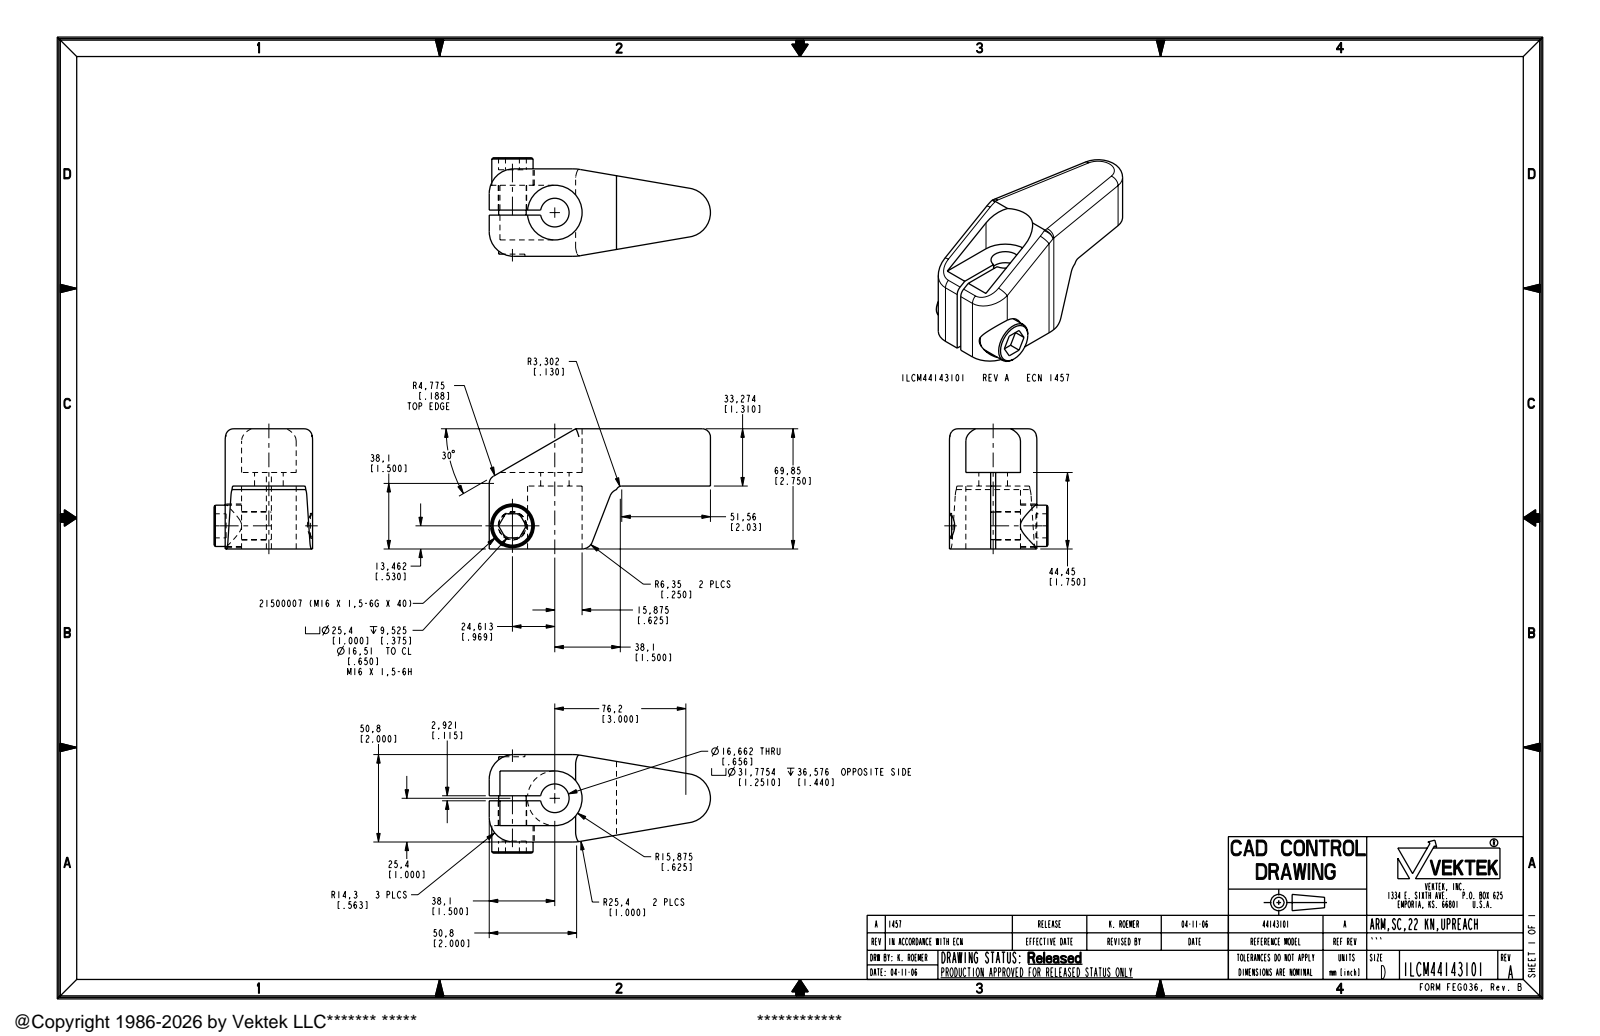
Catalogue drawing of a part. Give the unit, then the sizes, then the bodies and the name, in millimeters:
Units: millimetres
Overall size (bounding box): 128.6 × 69.85 × 57.27
Round holes (diameter × count): ⌀16.51 ×1, ⌀16.66 ×1, ⌀25.4 ×1, ⌀31.78 ×1
Round bosses / shafts (diameter × count): ⌀24 ×1, ⌀16 ×1
Partial cylindrical surfaces — rounded edges, fillets, slot ends (radius × count): R4.78 ×7, R14.3 ×3, R6.35 ×2, R3.3 ×1, R7.26 ×1, R15.88 ×1, R25.4 ×1
Main face-to-face distances: 33.27, 69.85, 36.58, 23.94, 26.86, 50.8, 25.4, 7.87, 44.45, 2.92
Volume: 209 147 mm³ · Surface area: 35 758 mm²
Bodies: 1 solid, 67 faces (30 planar, 28 cylindrical, 9 other)
Part name (STEP PRODUCT): ILCM44143101
STEP written by: PRO/ENGINEER BY PARAMETRIC TECHNOLOGY CORPORATION, 2004290 (AUTOMOTIVE_DESIGN_CC2)
